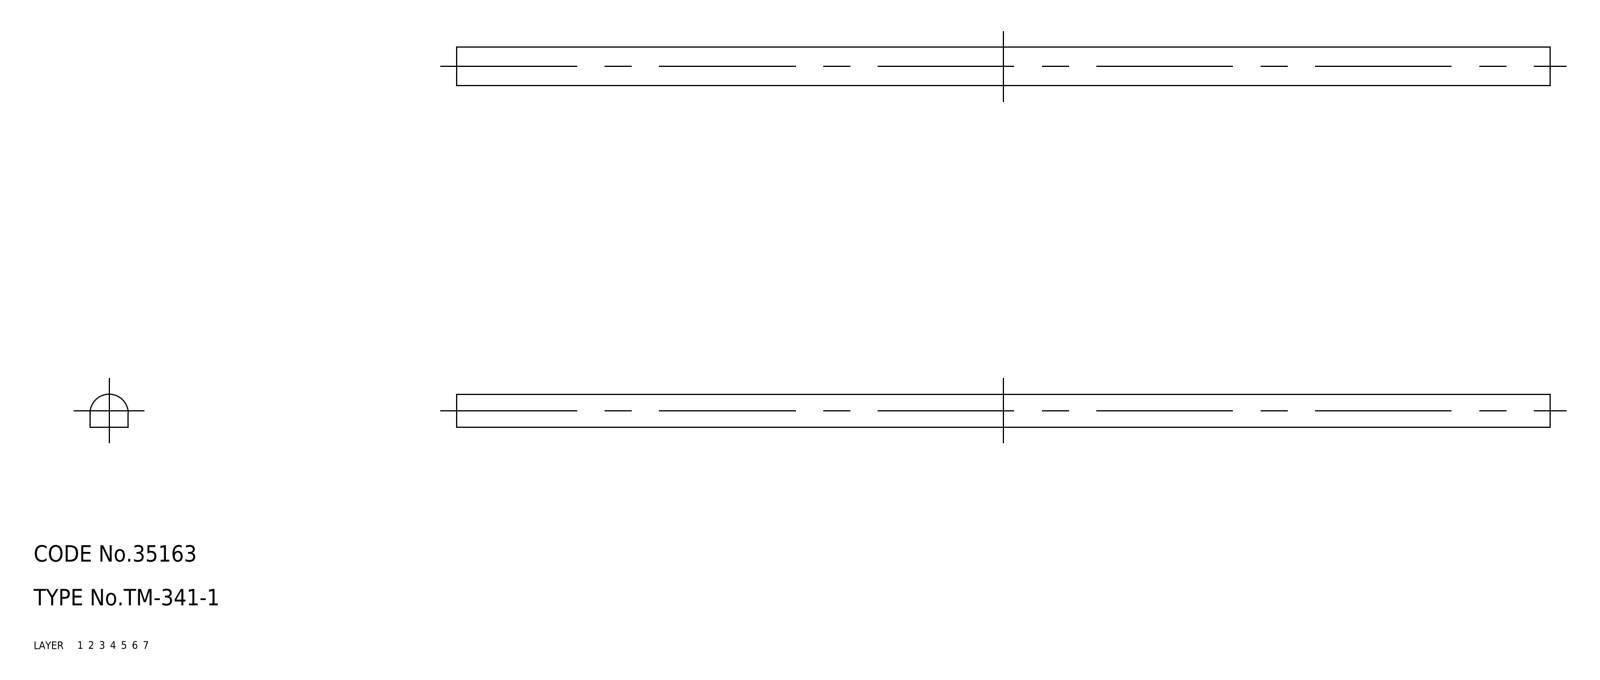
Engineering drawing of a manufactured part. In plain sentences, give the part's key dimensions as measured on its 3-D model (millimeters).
The part is named "rubber foam; TM_341_1". Its 3-D file was written by "SolidWorks 2015 (AUTOMOTIVE_DESIGN)". It is 1 solid with 6 faces: 5 planar, 1 cylindrical and 0 other. Overall it measures 200 by 7 by 6 millimeters. Its volume is 7 348 cubic millimeters and its surface area 4 673 square millimeters. Partial cylindrical surfaces (rounded edges, fillets, slot ends): 1 of radius 3.5. The main face-to-face distances are 7, 200.
